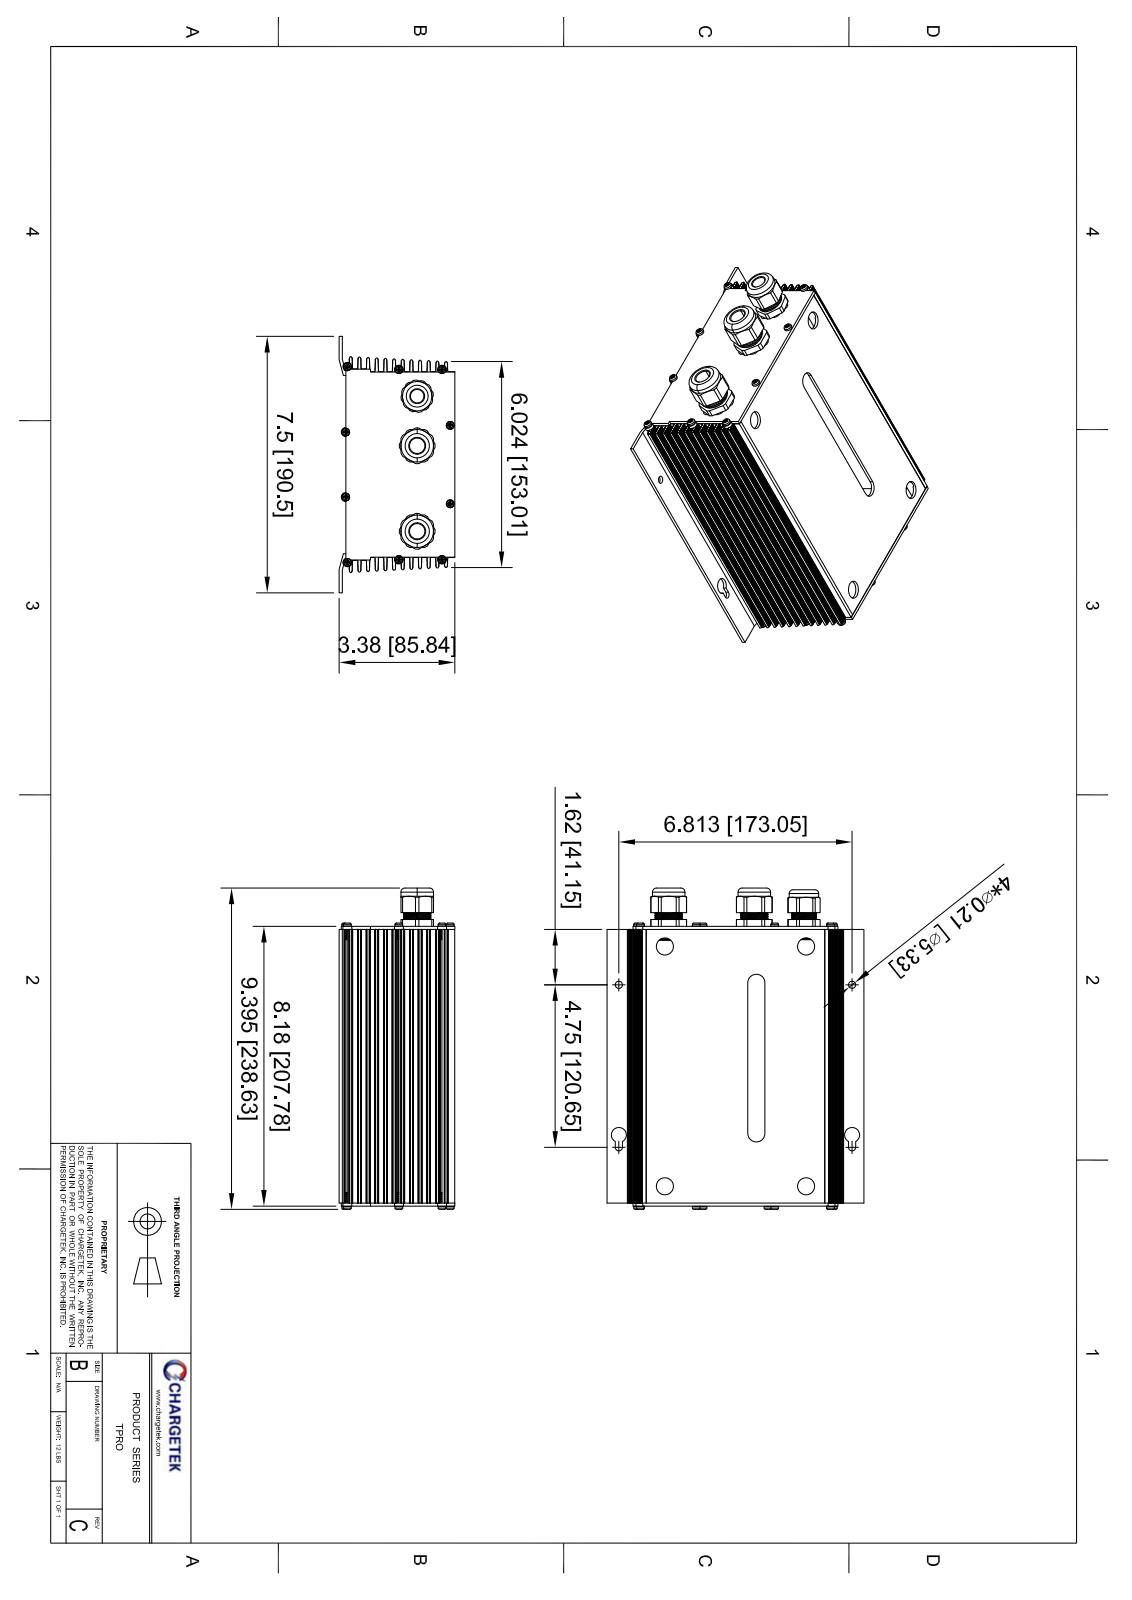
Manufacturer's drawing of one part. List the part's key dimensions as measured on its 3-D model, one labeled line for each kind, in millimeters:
Part name (STEP PRODUCT): 890-TPROT; 660-0079_Screw; 890-TPROB; 650-0033_heyco-m3213-m3214 (+4 more)
STEP written by: SolidWorks 2014 (CONFIG_CONTROL_DESIGN)
Units: millimetres
Bodies: 27 solids, 3291 faces (1493 planar, 1573 cylindrical, 225 other)
Overall size (bounding box): 238.63 × 190.5 × 85.84
Volume: 466 253 mm³ · Surface area: 382 769 mm²
Round holes (diameter × count): ⌀3.81 ×10, ⌀3 ×6, ⌀12.7 ×4, ⌀3 ×2, ⌀5.33 ×2, ⌀11.1 ×2, ⌀11.43 ×2, ⌀20.62 ×2, ⌀2.59 ×1, ⌀10.03 ×1, ⌀19.05 ×1
Round bosses / shafts (diameter × count): ⌀2.5 ×10, ⌀24.13 ×2, ⌀20.32 ×2, ⌀18.8 ×2, ⌀18.29 ×2, ⌀21.84 ×1, ⌀18.54 ×1, ⌀17.02 ×1
Partial cylindrical surfaces — rounded edges, fillets, slot ends (radius × count): R0.3 ×773, R0.5 ×80, R0.8 ×24, R2.77 ×8, R3.3 ×8, R1.5 ×2, R2.67 ×2, R2.75 ×2
Main face-to-face distances: 2.38, 76.96, 79.34, 2.29, 205.49, 77.04, 74.66, 2.3, 132.46, 2.79
Hole centre spacings: 32.01, 38.28, 41.84, 44.45, 48.53, 51.16, 56.25, 60.88
